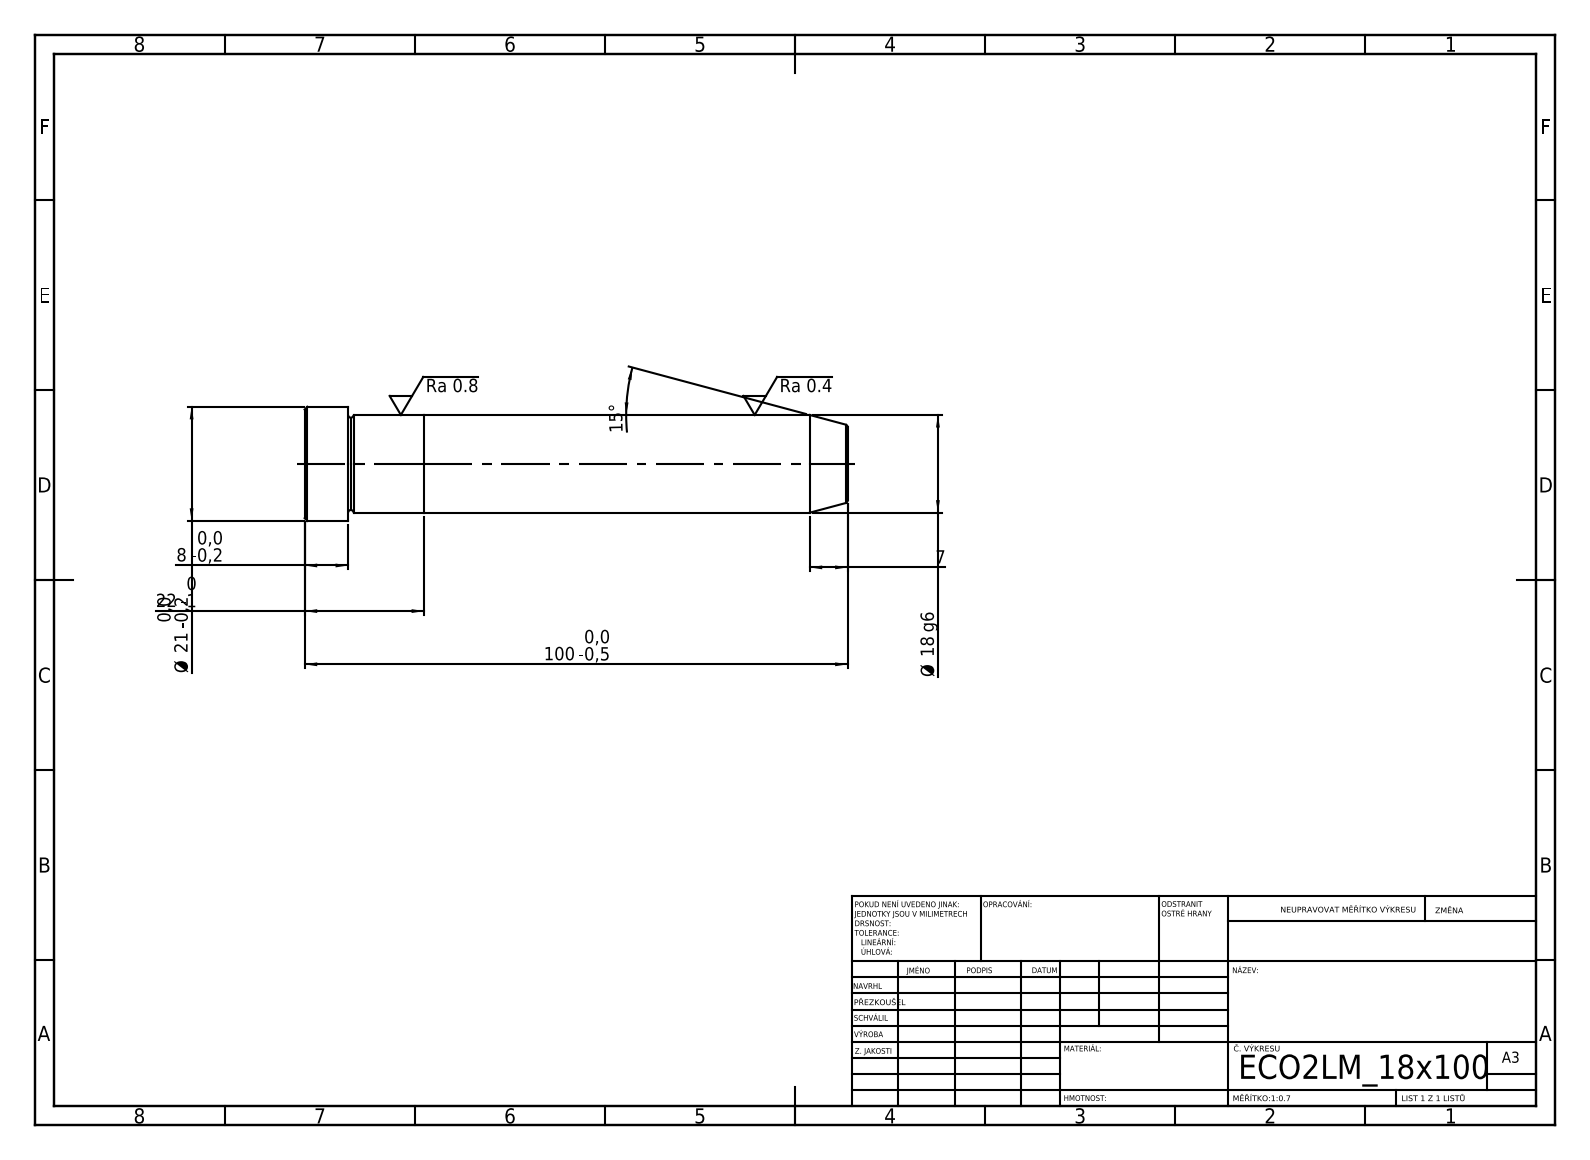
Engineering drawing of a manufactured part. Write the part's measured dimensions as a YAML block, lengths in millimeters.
step_written_by: "SolidWorks 2019 (CONFIG_CONTROL_DESIGN)"
units: millimeters
bodies: {solids: 2, faces: 21, planar: 5, cylindrical: 6, other: 10}
overall_size: [100, 21, 21]
volume: 25806
surface_area: 6813
round_bosses_or_shafts:
  - {diameter: 21, count: 1}
  - {diameter: 18, count: 1}
face_to_face_distances: [22, 78, 100, 92, 14, 8]
